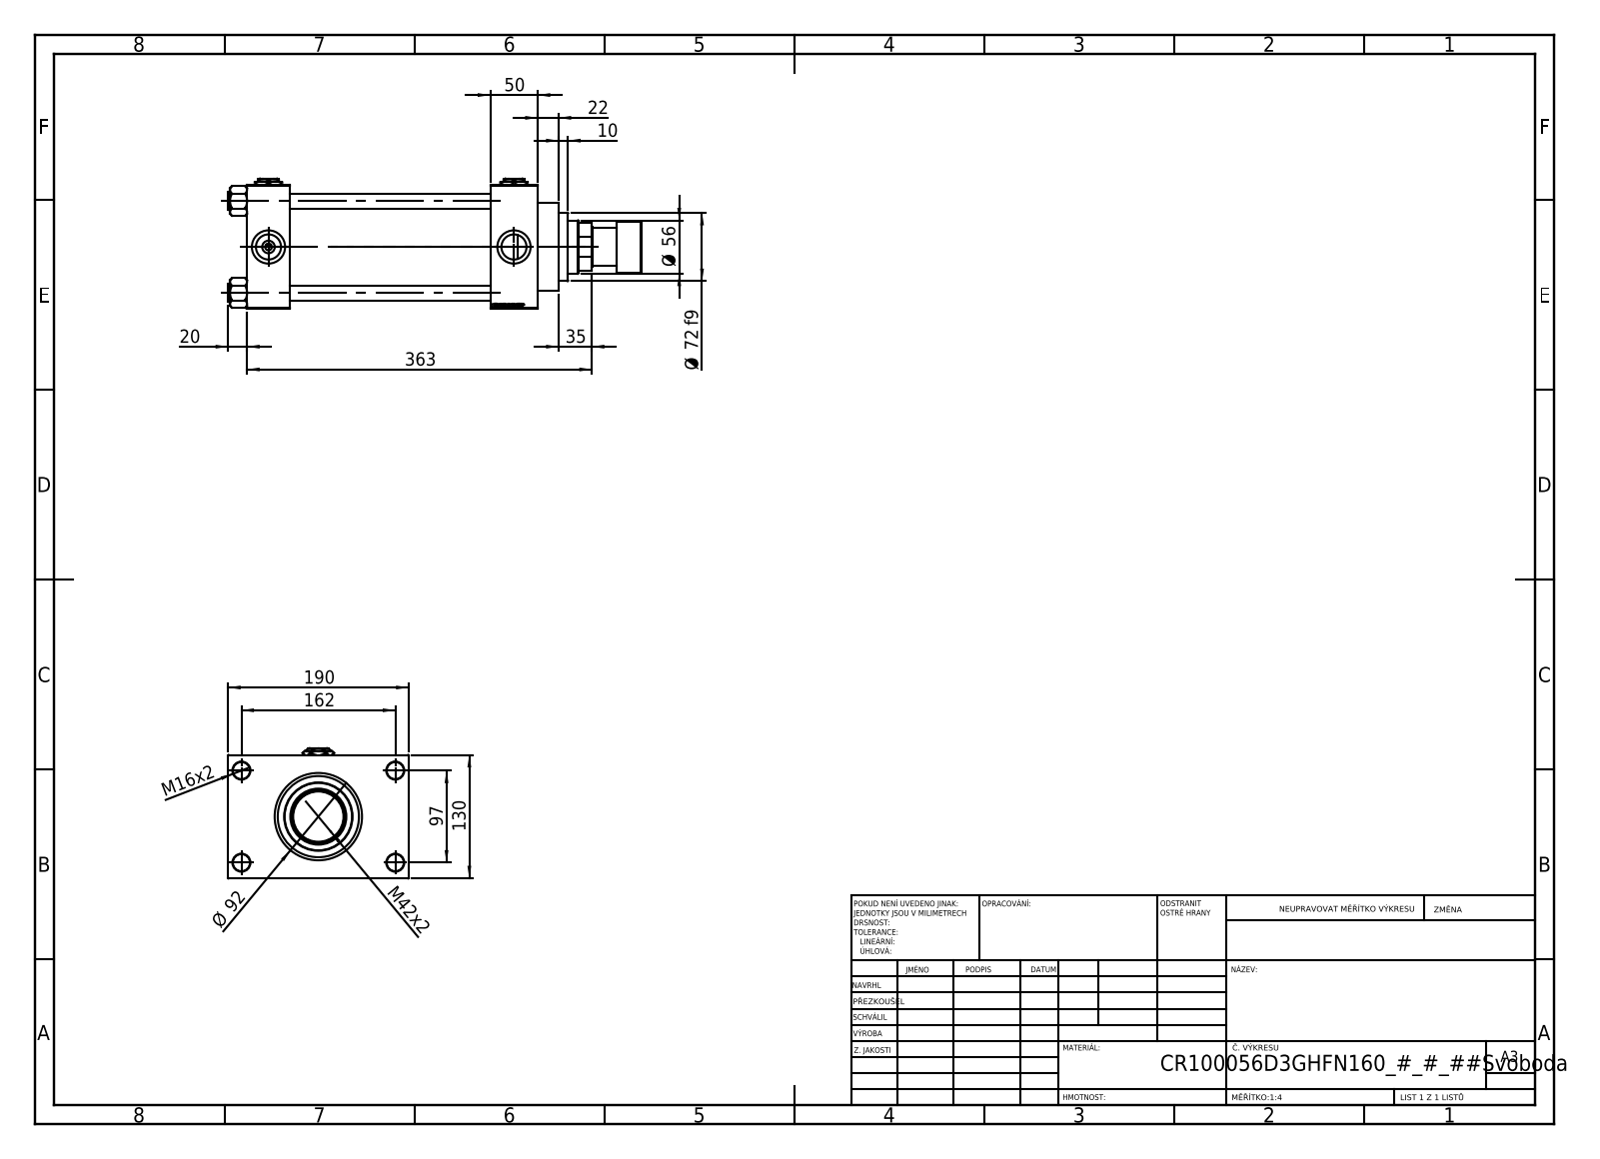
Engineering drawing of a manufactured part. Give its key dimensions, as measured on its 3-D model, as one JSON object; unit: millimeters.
{"part_name": "V215CR_D_TYCINKA; Zatka_pro_OIL_PORT; V215_VC_A; V215CR_ROD_END_F (+3 more)", "step_written_by": "SolidWorks 2019 (CONFIG_CONTROL_DESIGN)", "units": "millimeters", "bodies": {"solids": 14, "faces": 1266, "planar": 597, "cylindrical": 103, "other": 566}, "overall_size": [435, 190, 137], "volume_mm3": 3299000, "surface_area_mm2": 525205, "round_holes": [[16, 4], [18, 4], [26.44, 4], [35, 4], [7, 3], [40.5, 1], [56, 1], [59, 1], [76, 1], [85.5, 1], [100, 1]], "round_bosses_or_shafts": [[19, 4], [106, 1], [92, 1], [72, 1], [54, 1], [40, 1]], "face_to_face_distances": [130, 50, 45, 256, 211, 306, 261, 160, 30, 51], "hole_center_spacings": [32.55, 68.52, 94.41, 96.9, 102.27, 129.45, 161.73, 97]}
